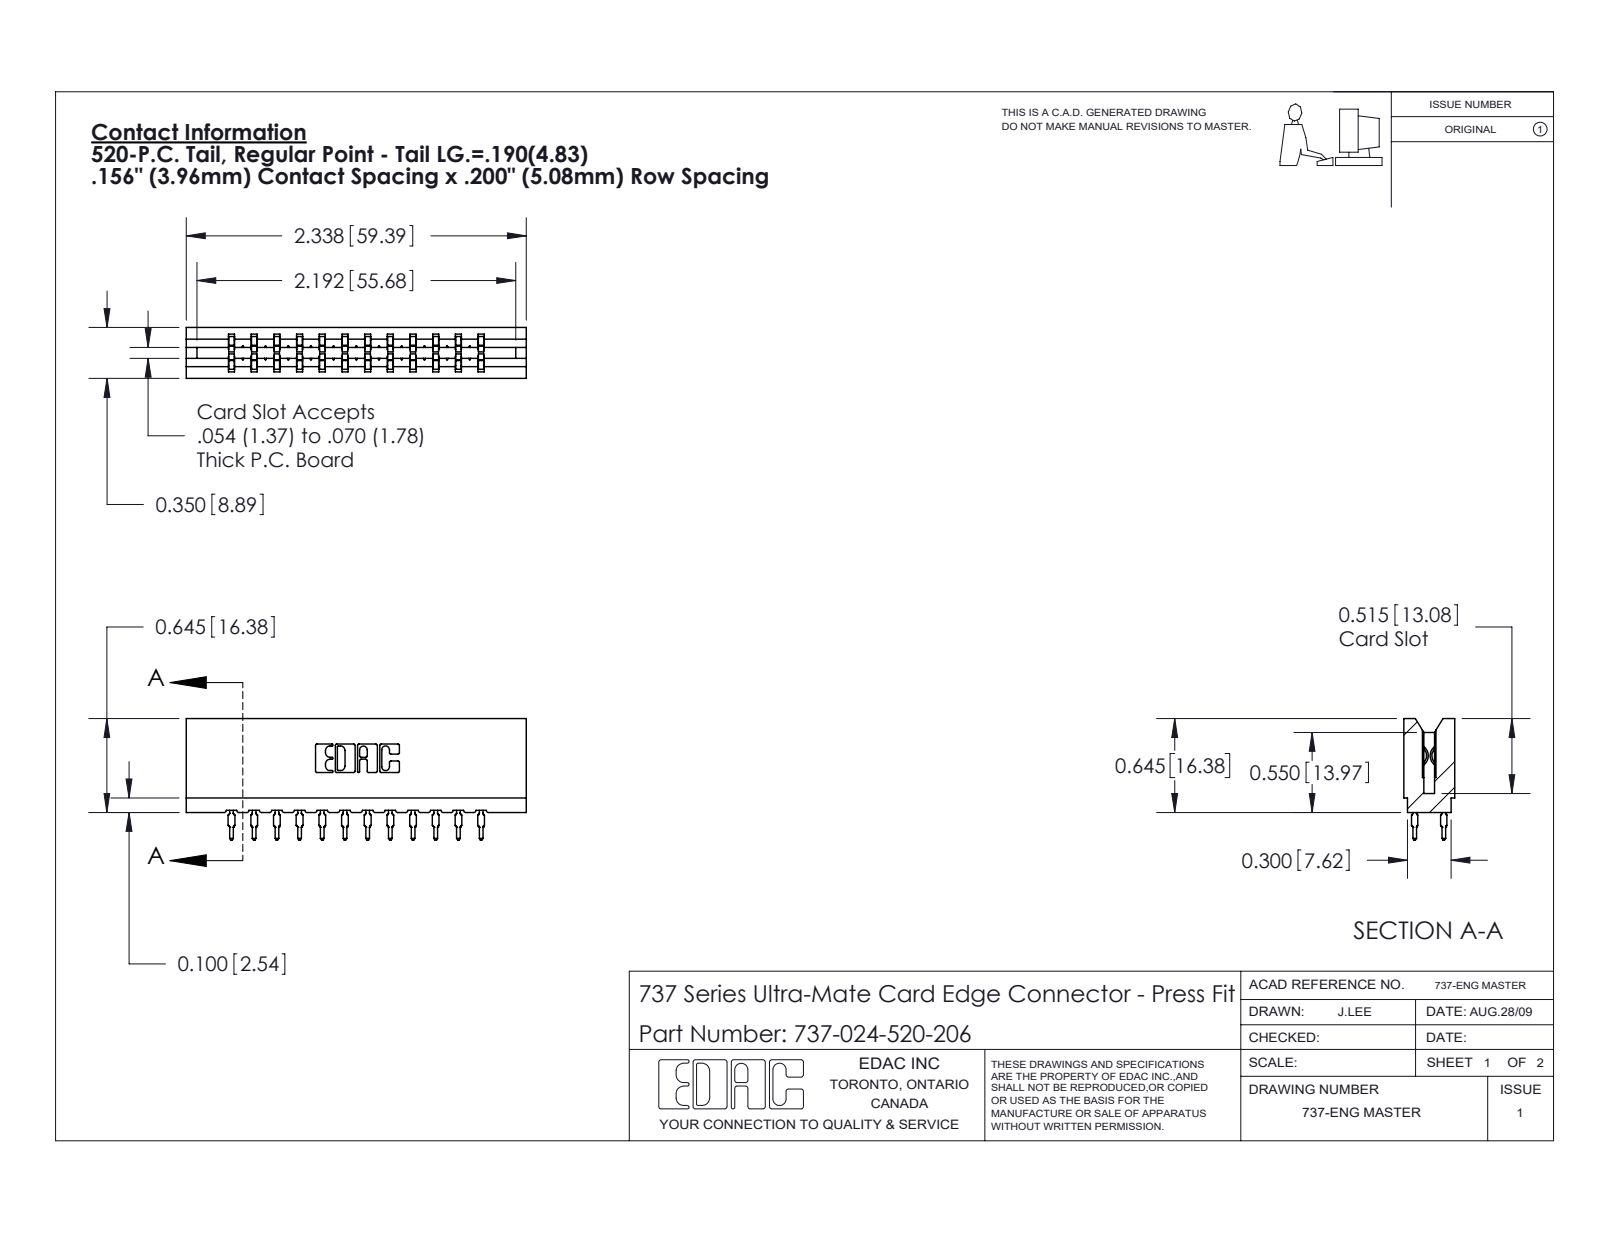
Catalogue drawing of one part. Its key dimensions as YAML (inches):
part_name: "737 Part_Insulator Option - 06; 745-292-001_520; 737-024-520-206"
step_written_by: "SolidWorks 2020 (CONFIG_CONTROL_DESIGN)"
units: inches
bodies: {solids: 25, faces: 2255, planar: 1171, cylindrical: 460, other: 624}
overall_size: [2.338, 0.836, 0.35]
volume: 0.367
surface_area: 12.34
partial_cylinders:
  - {radius: 0.021, count: 48}
  - {radius: 0.015, count: 24}
  - {radius: 0.01, count: 22}
  - {radius: 0.005, count: 8}
  - {radius: 0.011, count: 8}
  - {radius: 0.007, count: 6}
  - {radius: 0.031, count: 6}
  - {radius: 0.026, count: 3}
face_to_face_distances: [0.156, 0.138, 0.212, 0.35, 0.624, 0.312, 0.468, 0.78, 0.074, 0.354]
